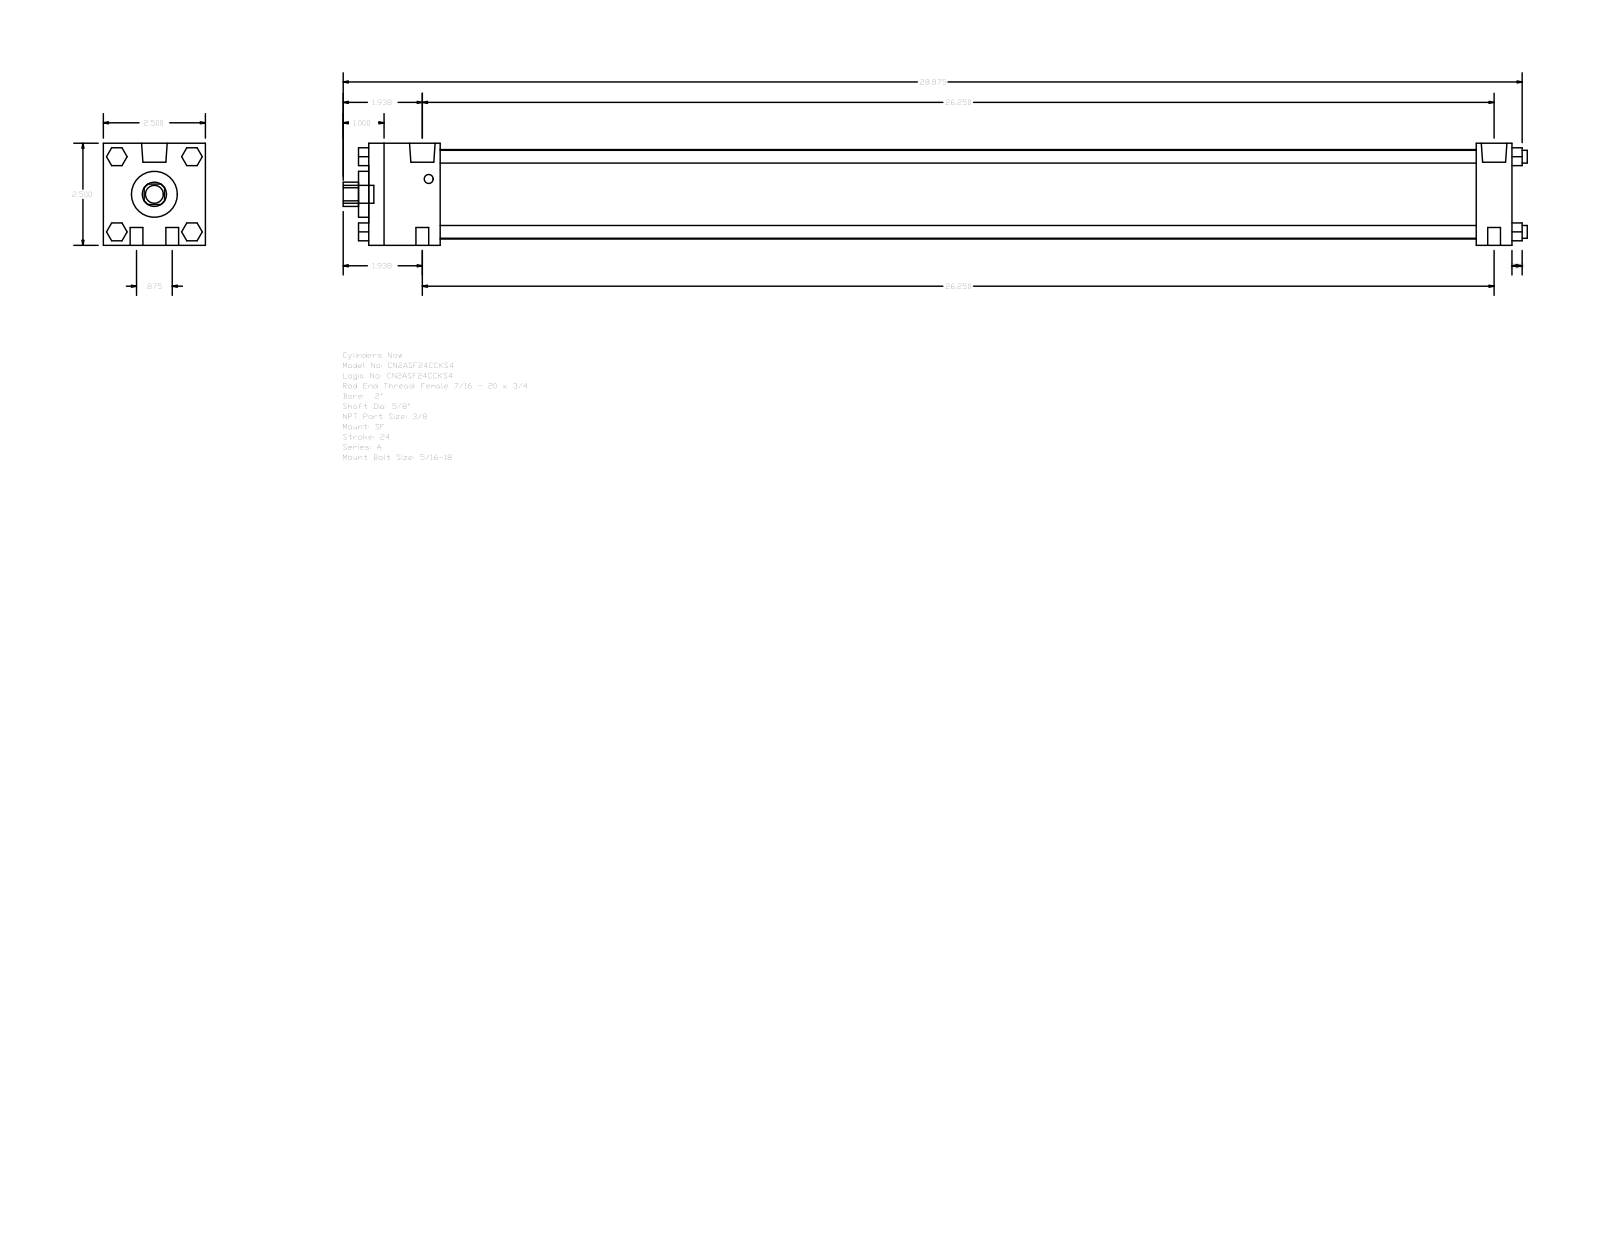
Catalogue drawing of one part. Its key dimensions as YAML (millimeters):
part_name: "A_SF__0200_0.625"
step_written_by: "GSSL Pune (CONFIG_CONTROL_DESIGN)"
units: millimeters
bodies: {solids: 0, faces: 124, planar: 94, cylindrical: 30, other: 0}
overall_size: [736.6, 63.5, 63.5]
round_holes:
  - {diameter: 15.88, count: 1}
  - {diameter: 28.57, count: 1}
  - {diameter: 55.63, count: 1}
round_bosses_or_shafts:
  - {diameter: 7.94, count: 8}
  - {diameter: 15.93, count: 2}
  - {diameter: 5.56, count: 2}
  - {diameter: 11.11, count: 1}
partial_cylinders:
  - {radius: 7.54, count: 1}
face_to_face_distances: [63.5, 711.2, 688.97, 22.23, 44.45, 644.52, 666.75, 50.8, 717.55, 6.35]
